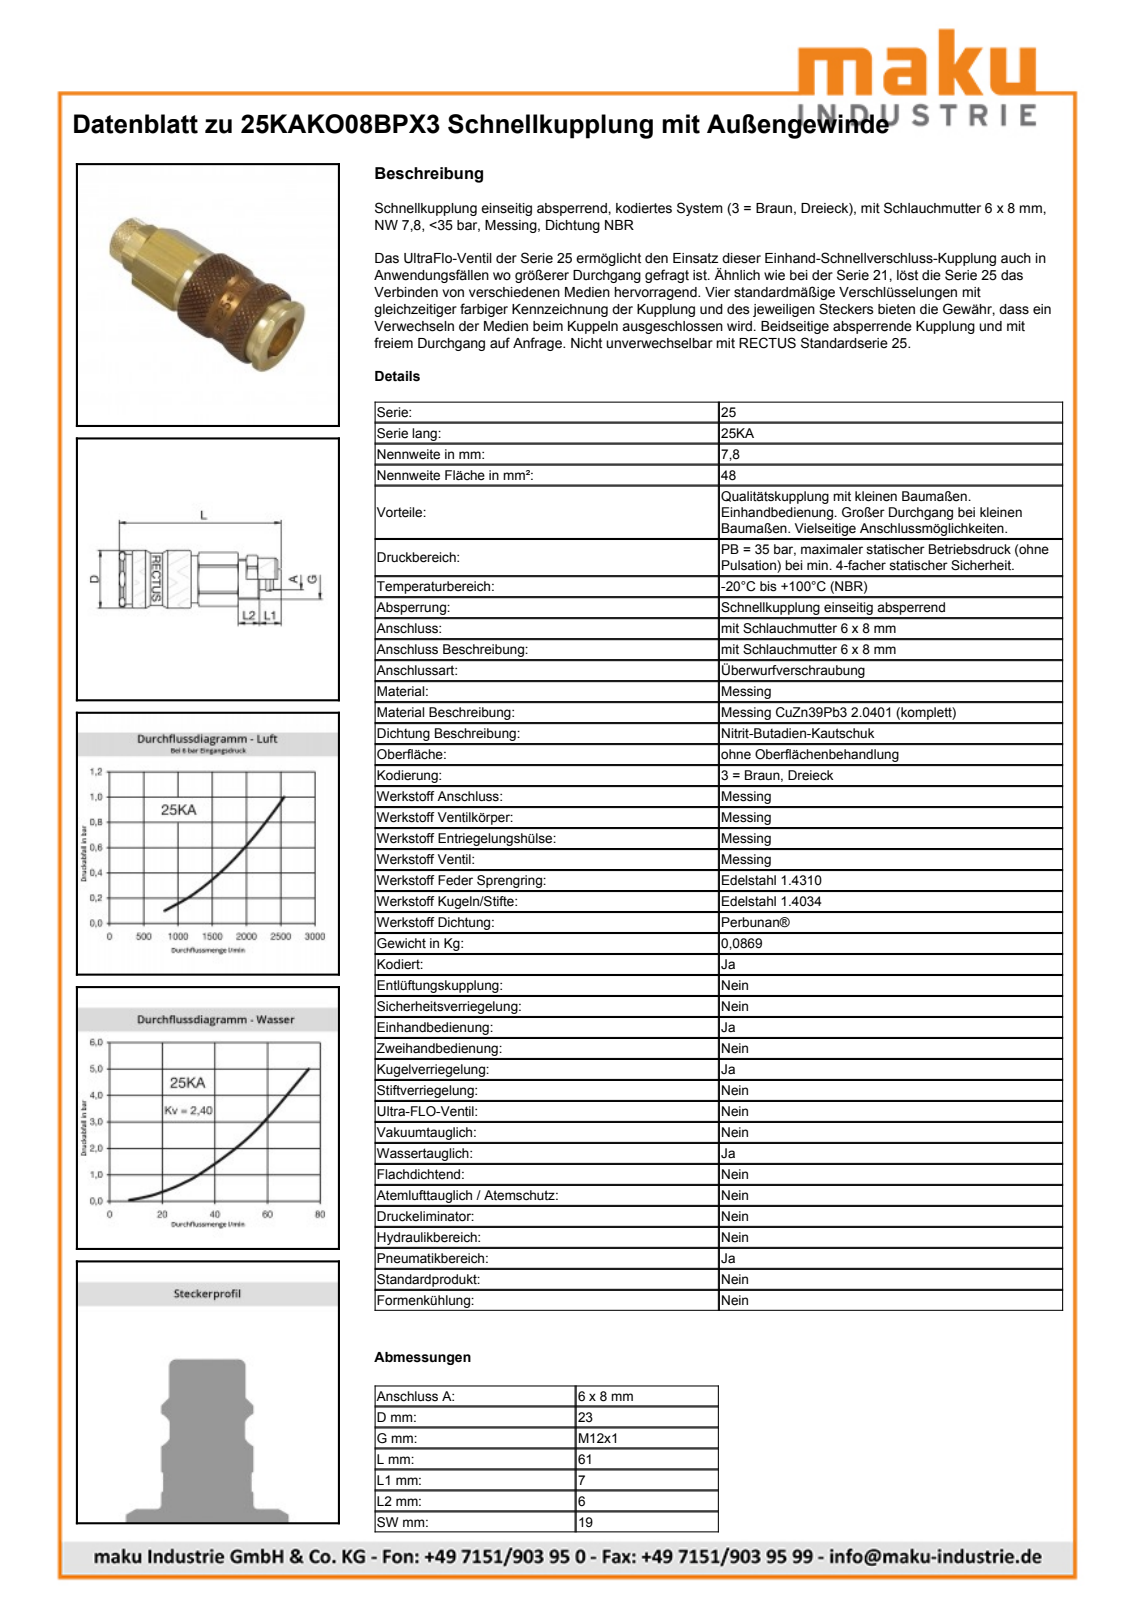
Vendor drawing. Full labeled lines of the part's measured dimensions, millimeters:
Part name (STEP PRODUCT): D111566
STEP written by: Autodesk Inventor 2013 (AUTOMOTIVE_DESIGN)
Units: millimetres
Bodies: 2 solids, 775 faces (261 planar, 95 cylindrical, 419 other)
Overall size (bounding box): 60.5 × 23.15 × 23.15
Volume: 17 061 mm³ · Surface area: 8 531 mm²
Round holes (diameter × count): ⌀8.25 ×1, ⌀11.15 ×1, ⌀15.1 ×1, ⌀15.6 ×1, ⌀17.25 ×1, ⌀19.35 ×1, ⌀20.05 ×1
Round bosses / shafts (diameter × count): ⌀23.15 ×1, ⌀21 ×1, ⌀20 ×1, ⌀18.95 ×1, ⌀16 ×1, ⌀15.3 ×1, ⌀15.06 ×1, ⌀14 ×1
Partial cylindrical surfaces — rounded edges, fillets, slot ends (radius × count): R7.75 ×1, R7.9 ×1, R10.4 ×1, R10.7 ×1, R11 ×1
Main face-to-face distances: 19, 47.25, 14, 24.5, 22.75, 53.4, 28.9, 6.15, 28.7, 4.2
